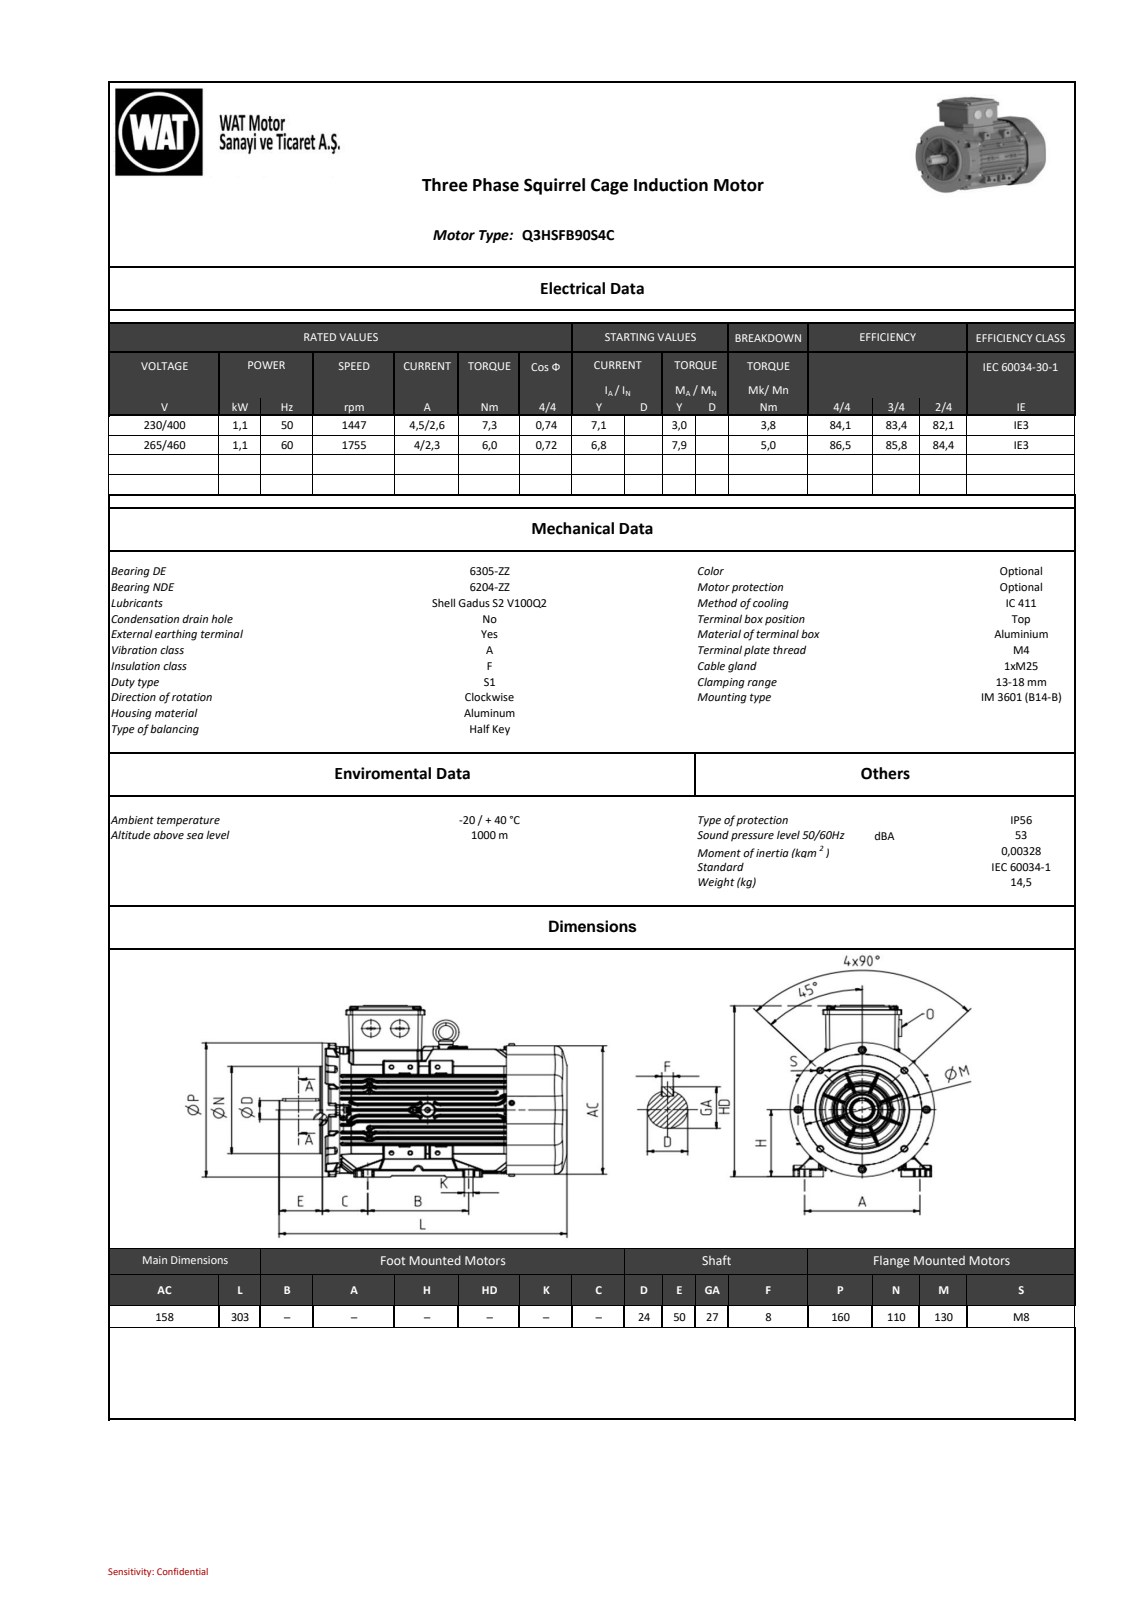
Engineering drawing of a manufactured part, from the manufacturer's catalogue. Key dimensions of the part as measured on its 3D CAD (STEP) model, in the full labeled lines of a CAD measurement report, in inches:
Part name (STEP PRODUCT): Ar311A3C0609zrs9
STEP written by: SIEMENS PLM Software NX 9.0 (AUTOMOTIVE_DESIGN)
Units: inches
Bodies: 0 solids, 7492 faces (1377 planar, 2218 cylindrical, 3897 other)
Overall size (bounding box): 11.929 × 7.935 × 6.304
Round holes (diameter × count): ⌀0.268 ×5, ⌀0.118 ×3, ⌀0.181 ×2, ⌀0.138 ×1, ⌀0.157 ×1, ⌀0.163 ×1, ⌀0.201 ×1, ⌀0.217 ×1, ⌀0.315 ×1, ⌀0.331 ×1, ⌀0.787 ×1, ⌀0.795 ×1
Round bosses / shafts (diameter × count): ⌀0.236 ×8, ⌀0.366 ×4, ⌀0.328 ×4, ⌀0.362 ×2, ⌀5.768 ×1, ⌀4.331 ×1, ⌀2.402 ×1, ⌀1.85 ×1
Partial cylindrical surfaces — rounded edges, fillets, slot ends (radius × count): R0.02 ×910, R0.031 ×330, R0.039 ×183, R0.028 ×62, R0.079 ×25, R0.157 ×14, R0.197 ×11, R0.004 ×10
Main face-to-face distances: 5.433, 0.039, 1.22, 8.701, 6.654, 1.555, 1.594, 1.652, 1.831, 1.437
Hole centre spacings: 1.004, 2.559, 3.619, 1.61, 1.739, 1.981, 2.495, 2.556
